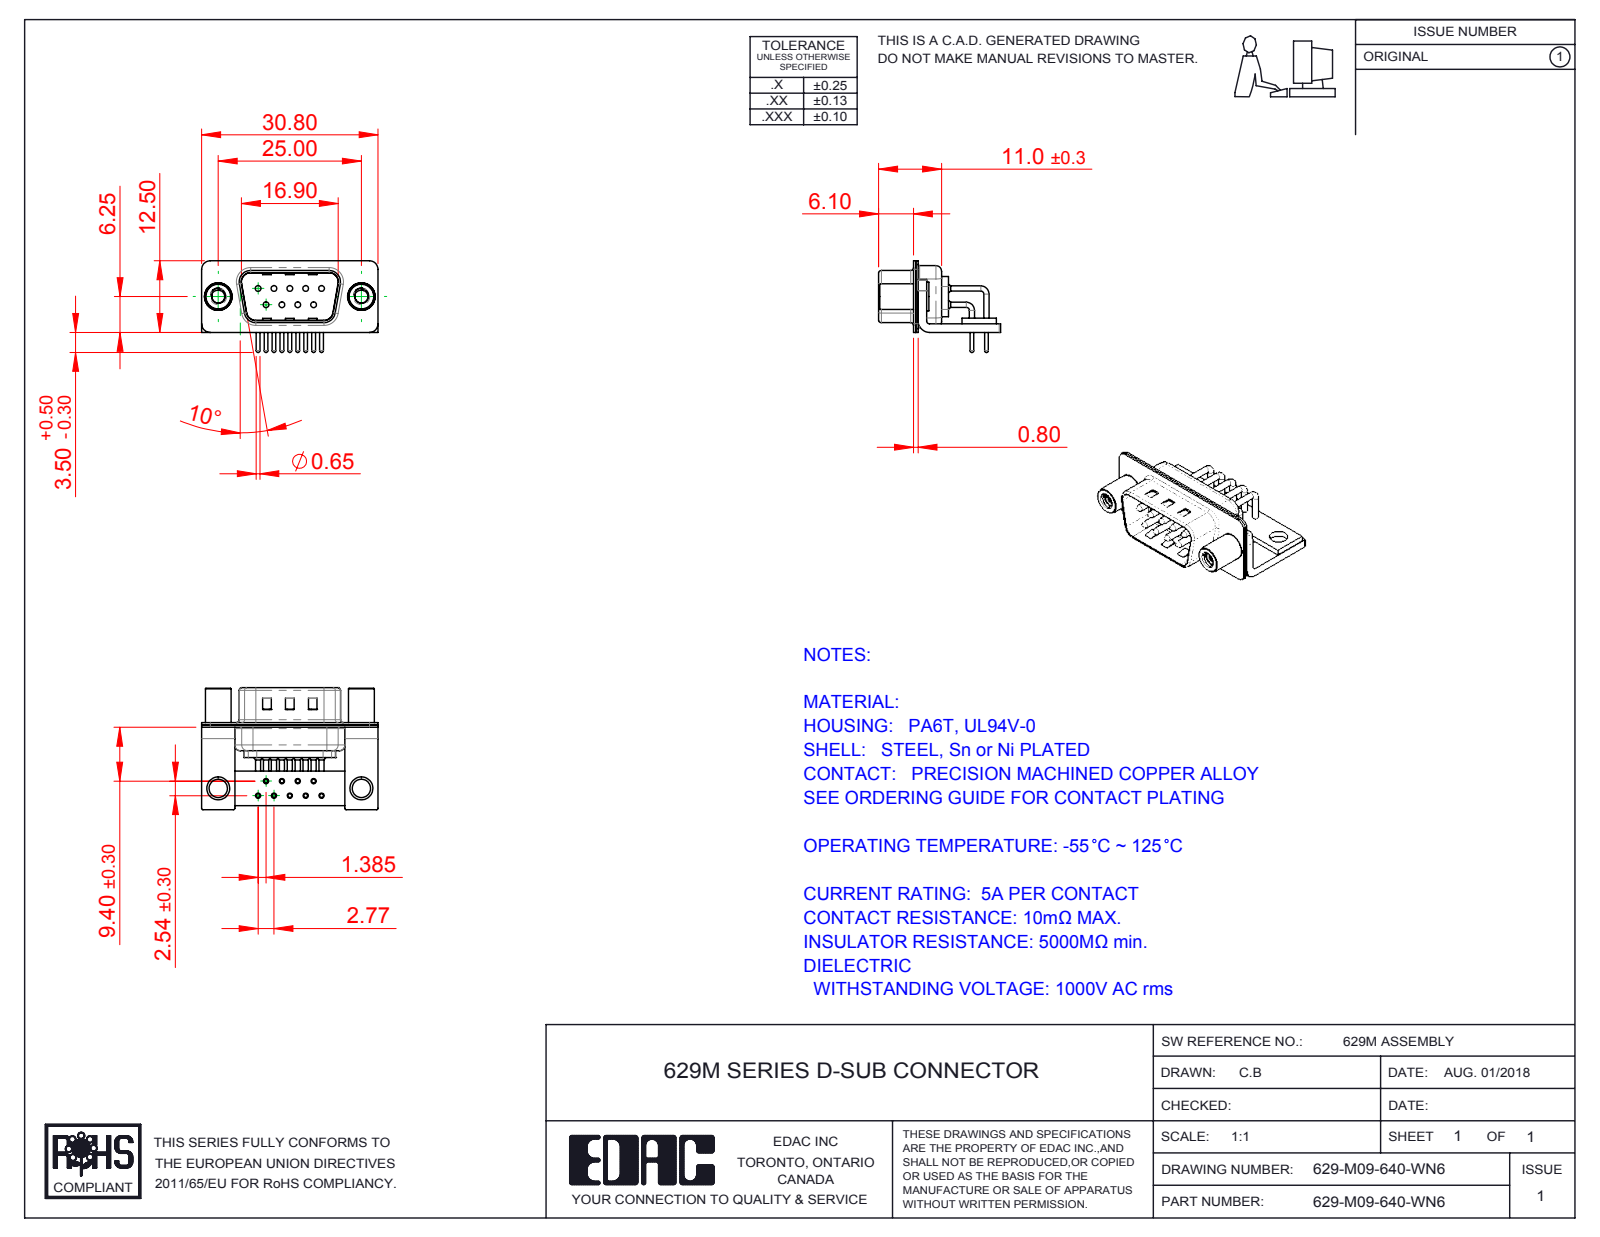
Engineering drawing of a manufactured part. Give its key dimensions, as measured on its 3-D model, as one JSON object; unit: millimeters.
{"part_name": "629-M09-640-WN6; 629M Stabilizer Board_09 Contacts; 629M Shell Rear_09 Contacts; 629M Contact Row 2 (+5 more)", "step_written_by": "SolidWorks 2016 (CONFIG_CONTROL_DESIGN)", "units": "millimeters", "bodies": {"solids": 17, "faces": 1412, "planar": 711, "cylindrical": 535, "other": 166}, "overall_size": [30.8, 21.3, 16], "volume_mm3": 1938, "surface_area_mm2": 5267, "round_holes": [[0.9, 9], [1, 9], [1.7, 9], [2, 9], [2.26, 2], [3.2, 2], [4, 2], [4.8, 2]], "round_bosses_or_shafts": [[1.5, 9], [0.9, 9], [0.65, 9], [5, 2], [4.9, 2], [4.5, 2]], "partial_cylinders_radius": [[0.25, 16], [1.5, 16], [2, 13], [0.5, 9], [1.01, 9], [1.6, 8], [0.6, 4], [0.65, 4]], "face_to_face_distances": [0.4, 1.5, 0.8, 0.85, 1.25, 1.9, 1, 2.5, 10.4, 9.55], "hole_center_spacings": [2.77, 5.54, 3.16, 4.87, 8.31, 2.89, 2.9, 5.03]}
